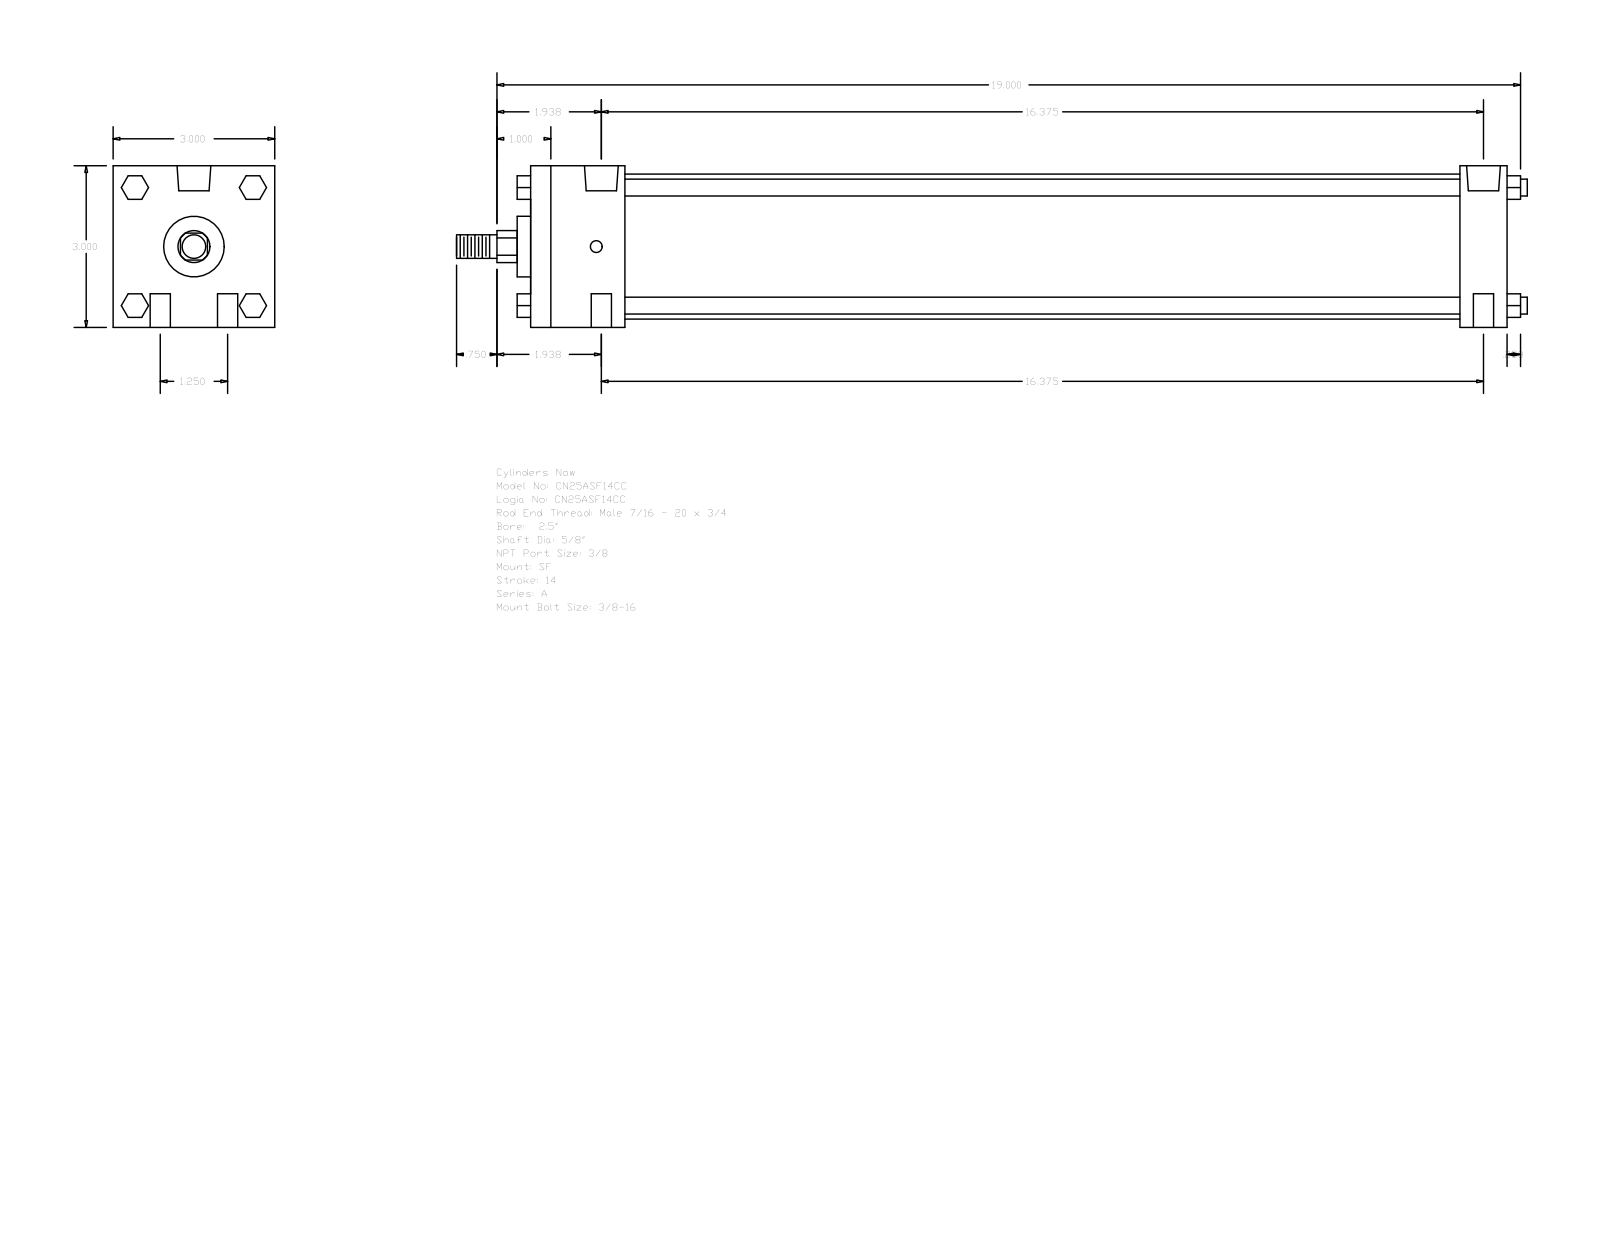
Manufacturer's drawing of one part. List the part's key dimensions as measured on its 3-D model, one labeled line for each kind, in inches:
Part name (STEP PRODUCT): A_SF__0250_0.625
STEP written by: GSSL Pune (CONFIG_CONTROL_DESIGN)
Units: inches
Bodies: 0 solids, 124 faces (94 planar, 30 cylindrical, 0 other)
Overall size (bounding box): 19.875 × 3 × 3
Round holes (diameter × count): ⌀0.375 ×4, ⌀0.219 ×2, ⌀0.627 ×2
Round bosses / shafts (diameter × count): ⌀0.313 ×4, ⌀2.69 ×1, ⌀1.125 ×1, ⌀0.625 ×1, ⌀0.437 ×1
Partial cylindrical surfaces — rounded edges, fillets, slot ends (radius × count): R0.297 ×1
Main face-to-face distances: 3, 18.125, 1.75, 17.25, 0.875, 15.5, 16.375, 0.25, 18.375, 2
Hole centre spacings: 0.625, 16.387, 16.375, 1.25, 16.423, 16.563
